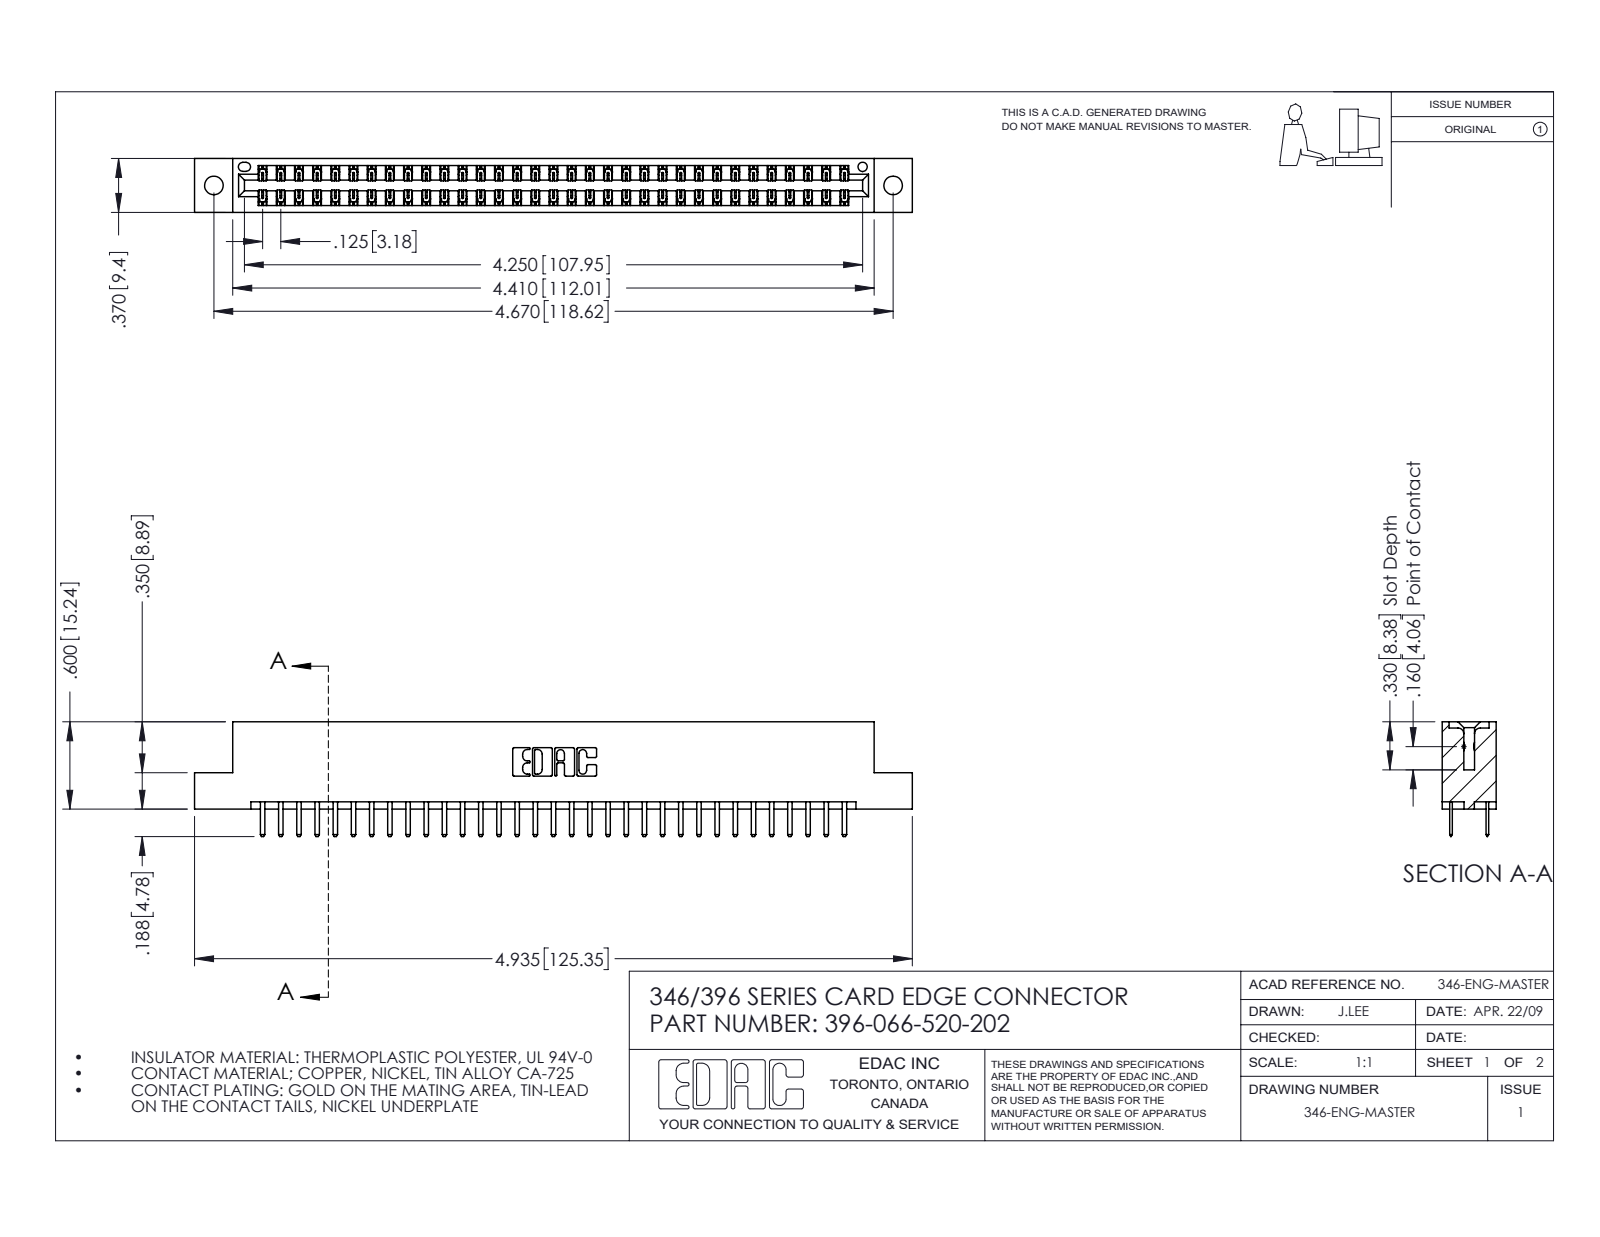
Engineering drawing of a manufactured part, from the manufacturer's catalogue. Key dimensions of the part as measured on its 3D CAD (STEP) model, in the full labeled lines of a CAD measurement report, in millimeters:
Part name (STEP PRODUCT): 396-066-520-202; 345-292-001_345-293-120; 346 Part_Flush Mounting Lugs - 0.128 Dia
STEP written by: SolidWorks 2016 (CONFIG_CONTROL_DESIGN)
Units: millimetres
Bodies: 67 solids, 3818 faces (2518 planar, 1300 cylindrical, 0 other)
Overall size (bounding box): 125.3 × 20 × 9.4
Volume: 12 100 mm³ · Surface area: 16 140 mm²
Round holes (diameter × count): ⌀3.3 ×2, ⌀1.6 ×1
Partial cylindrical surfaces — rounded edges, fillets, slot ends (radius × count): R0.2 ×99, R0.3 ×70, R0.3 ×22, R0.2 ×6, R0.8 ×6, R0.7 ×3, R0.4 ×2, R0.6 ×2
Main face-to-face distances: 1.2, 8.2, 6.4, 9.4, 7, 1.8, 7.6, 0.6, 3.8, 5.6
Hole centre spacings: 6.2, 113.3, 118.6
